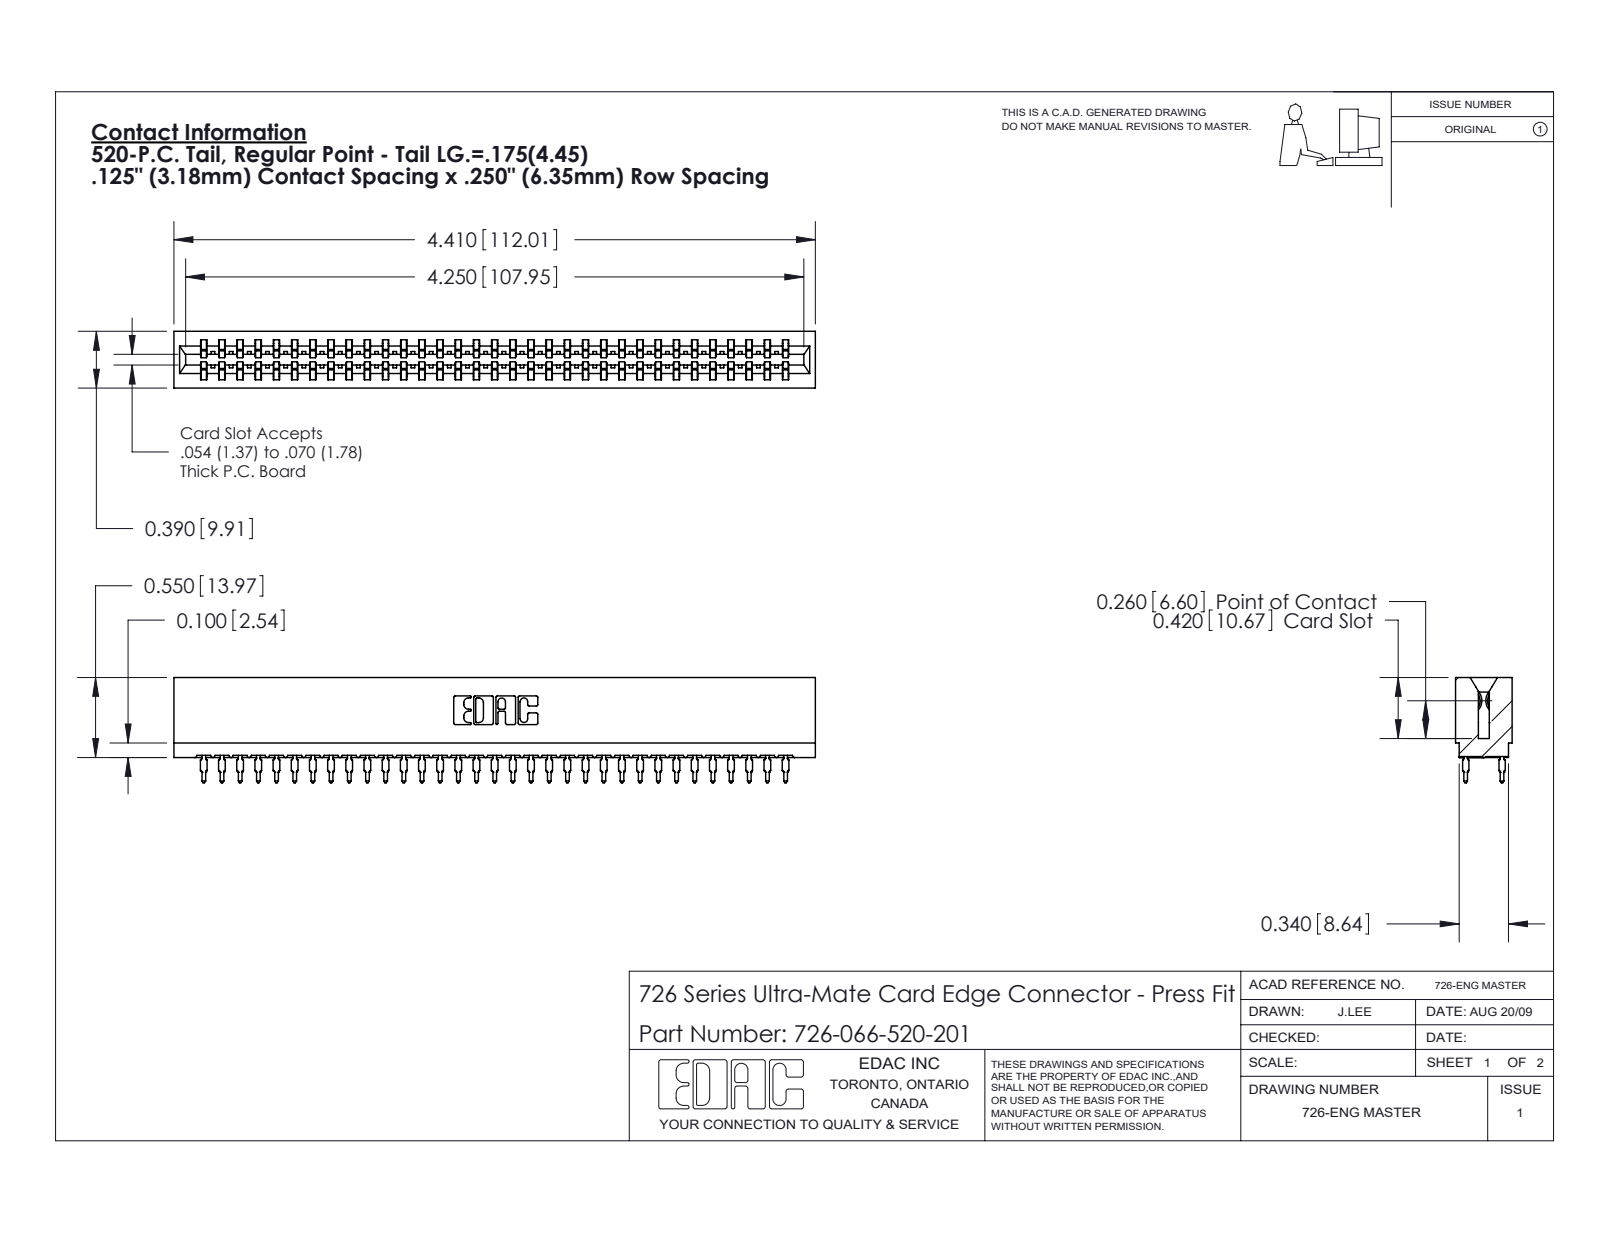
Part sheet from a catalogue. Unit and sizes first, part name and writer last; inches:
Units: inches
Overall size (bounding box): 4.41 × 0.724 × 0.39
Partial cylindrical surfaces — rounded edges, fillets, slot ends (radius × count): R0.021 ×132, R0.015 ×34, R0.01 ×22, R0.005 ×8, R0.011 ×8, R0.007 ×6, R0.031 ×6, R0.026 ×3
Main face-to-face distances: 0.057, 0.333, 0.25, 0.39, 0.025, 0.307, 0.275, 0.083, 0.5, 0.75
Volume: 0.629 in³ · Surface area: 25.91 in²
Bodies: 67 solids, 6004 faces (3091 planar, 1197 cylindrical, 1716 other)
Part name (STEP PRODUCT): 726 Part_.515 Slot Depth - 01; 726-066-520-201; 746-292-001_520
STEP written by: SolidWorks 2020 (CONFIG_CONTROL_DESIGN)
